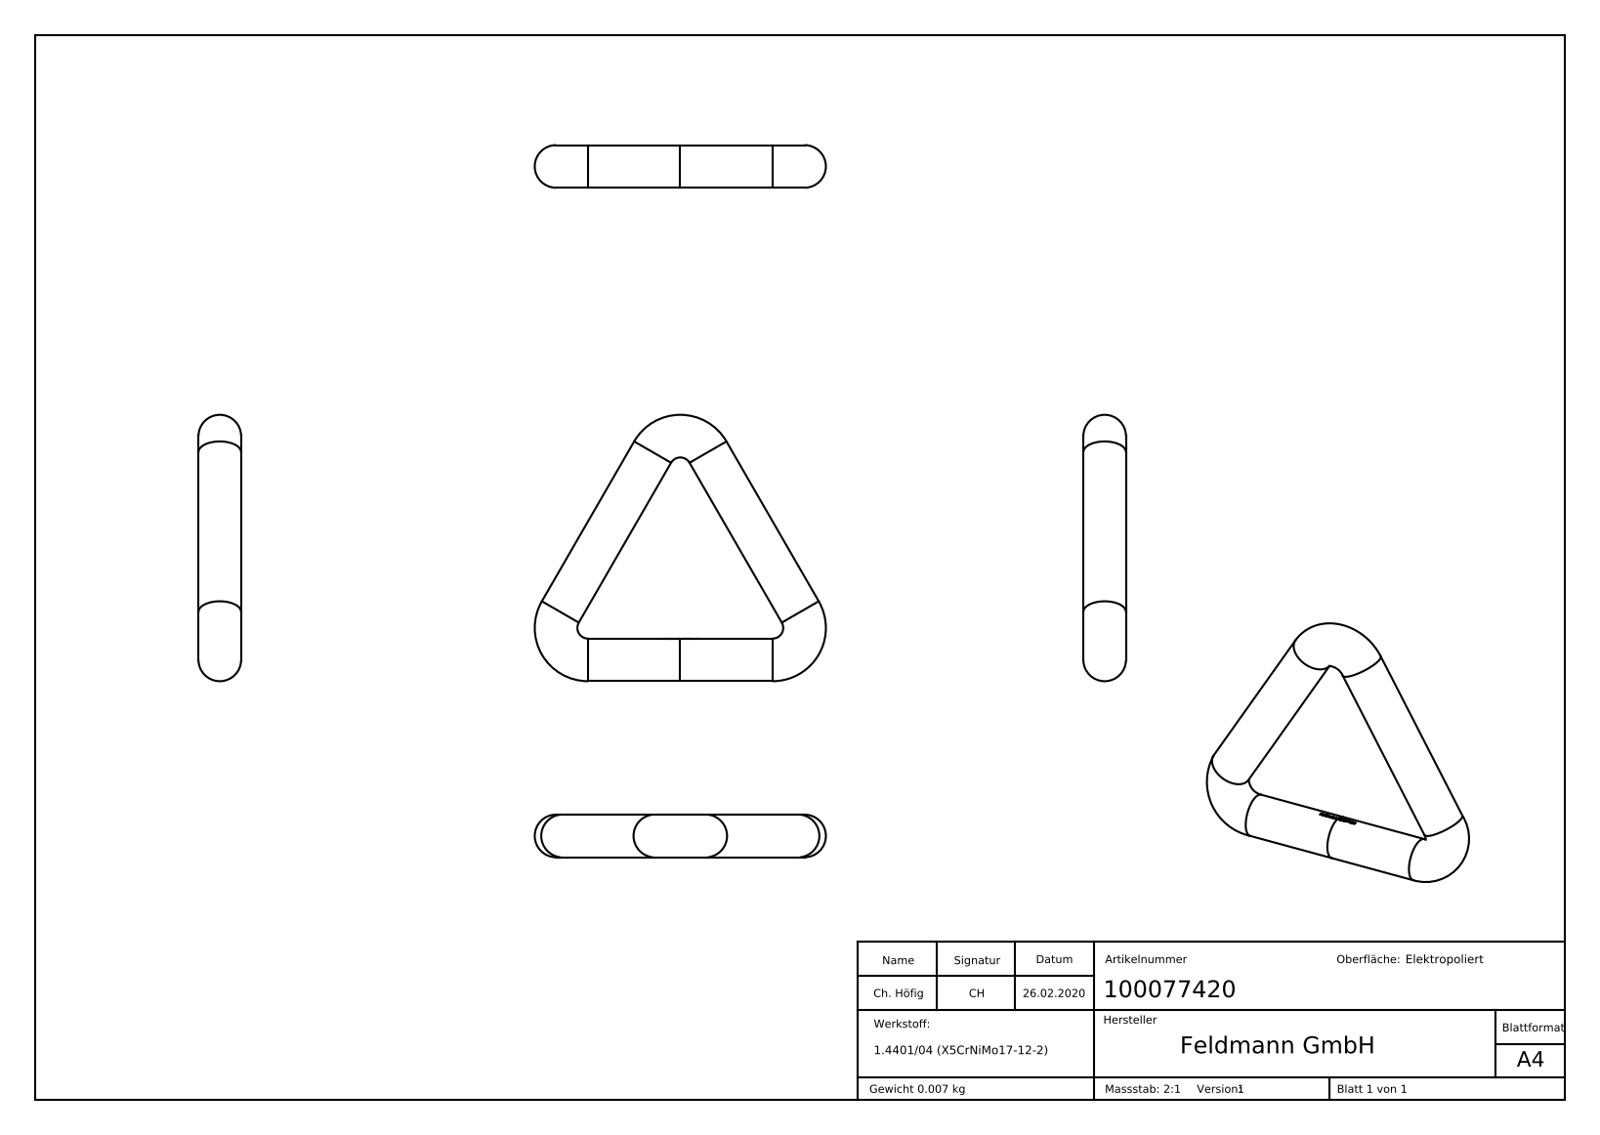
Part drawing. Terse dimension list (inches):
name: 100077420
written by: SolidWorks 2015 (CONFIG_CONTROL_DESIGN)
unit: in
bodies: 1 solid, 213 faces (91 planar, 29 cylindrical, 93 other)
size: 1.076 × 0.984 × 0.157
volume: 0.054 in³; area: 1.38 in²
bosses: 3× ⌀0.157
rounds: 1× R0.075
face distances: 0.023, 0.024, 0.013, 0.061, 0.016, 0.077, 0.076, 0.026, 0.05, 0.05
